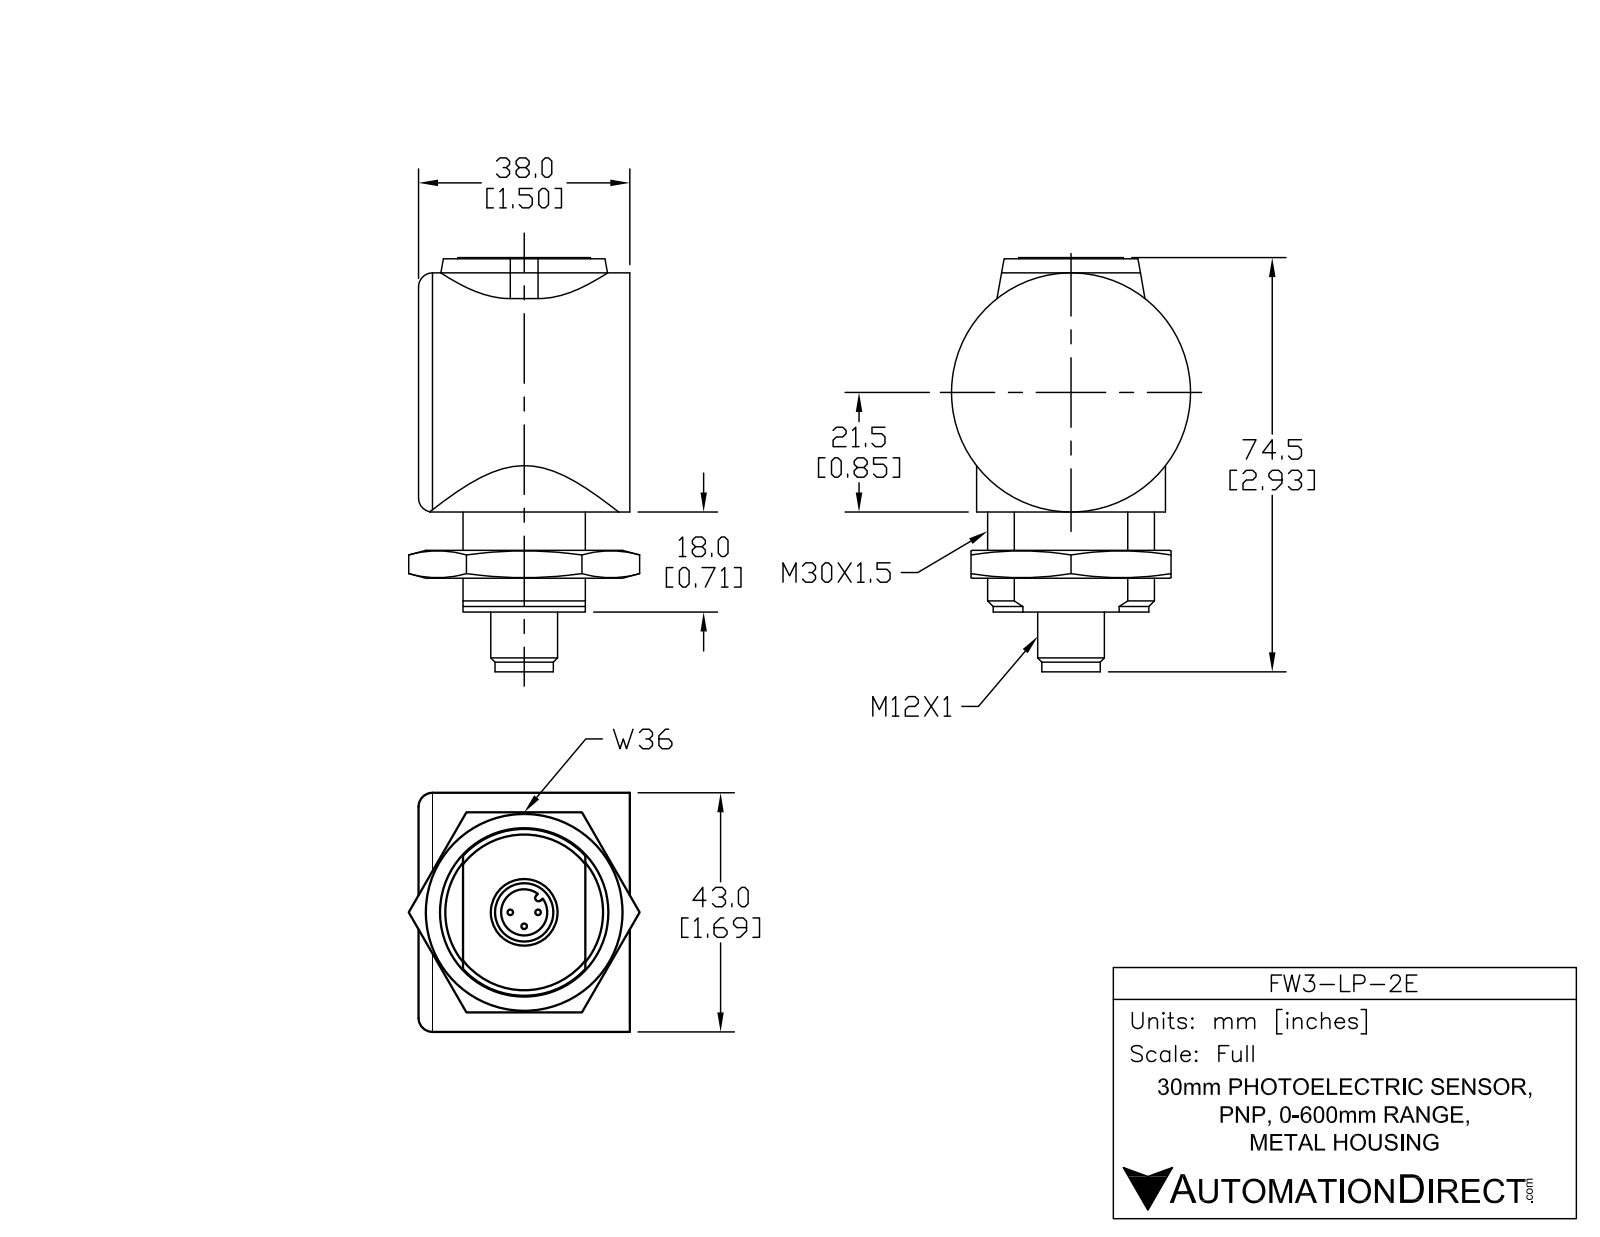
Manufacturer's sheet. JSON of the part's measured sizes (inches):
{"part_name": "FW3-LP-2E", "step_written_by": "SolidWorks 2013 (AUTOMOTIVE_DESIGN)", "units": "inches", "bodies": {"solids": 1, "faces": 201, "planar": 111, "cylindrical": 35, "other": 55}, "overall_size": [2.928, 1.69, 1.49], "volume_in3": 4.301, "surface_area_in2": 19.68, "round_holes": [[0.172, 1], [0.315, 1], [1.58, 1]], "round_bosses_or_shafts": [[0.04, 3], [1.69, 1], [0.47, 1], [0.39, 1], [0.18, 1]], "partial_cylinders_radius": [[0.48, 2], [0.64, 2], [0.025, 1], [0.408, 1], [0.492, 1], [0.545, 1], [0.587, 1]], "face_to_face_distances": [1.44, 2.498, 0.11, 2.388, 0.3, 0.19, 2.198, 1.178, 0.262, 0.312], "hole_center_spacings": [0.349]}
